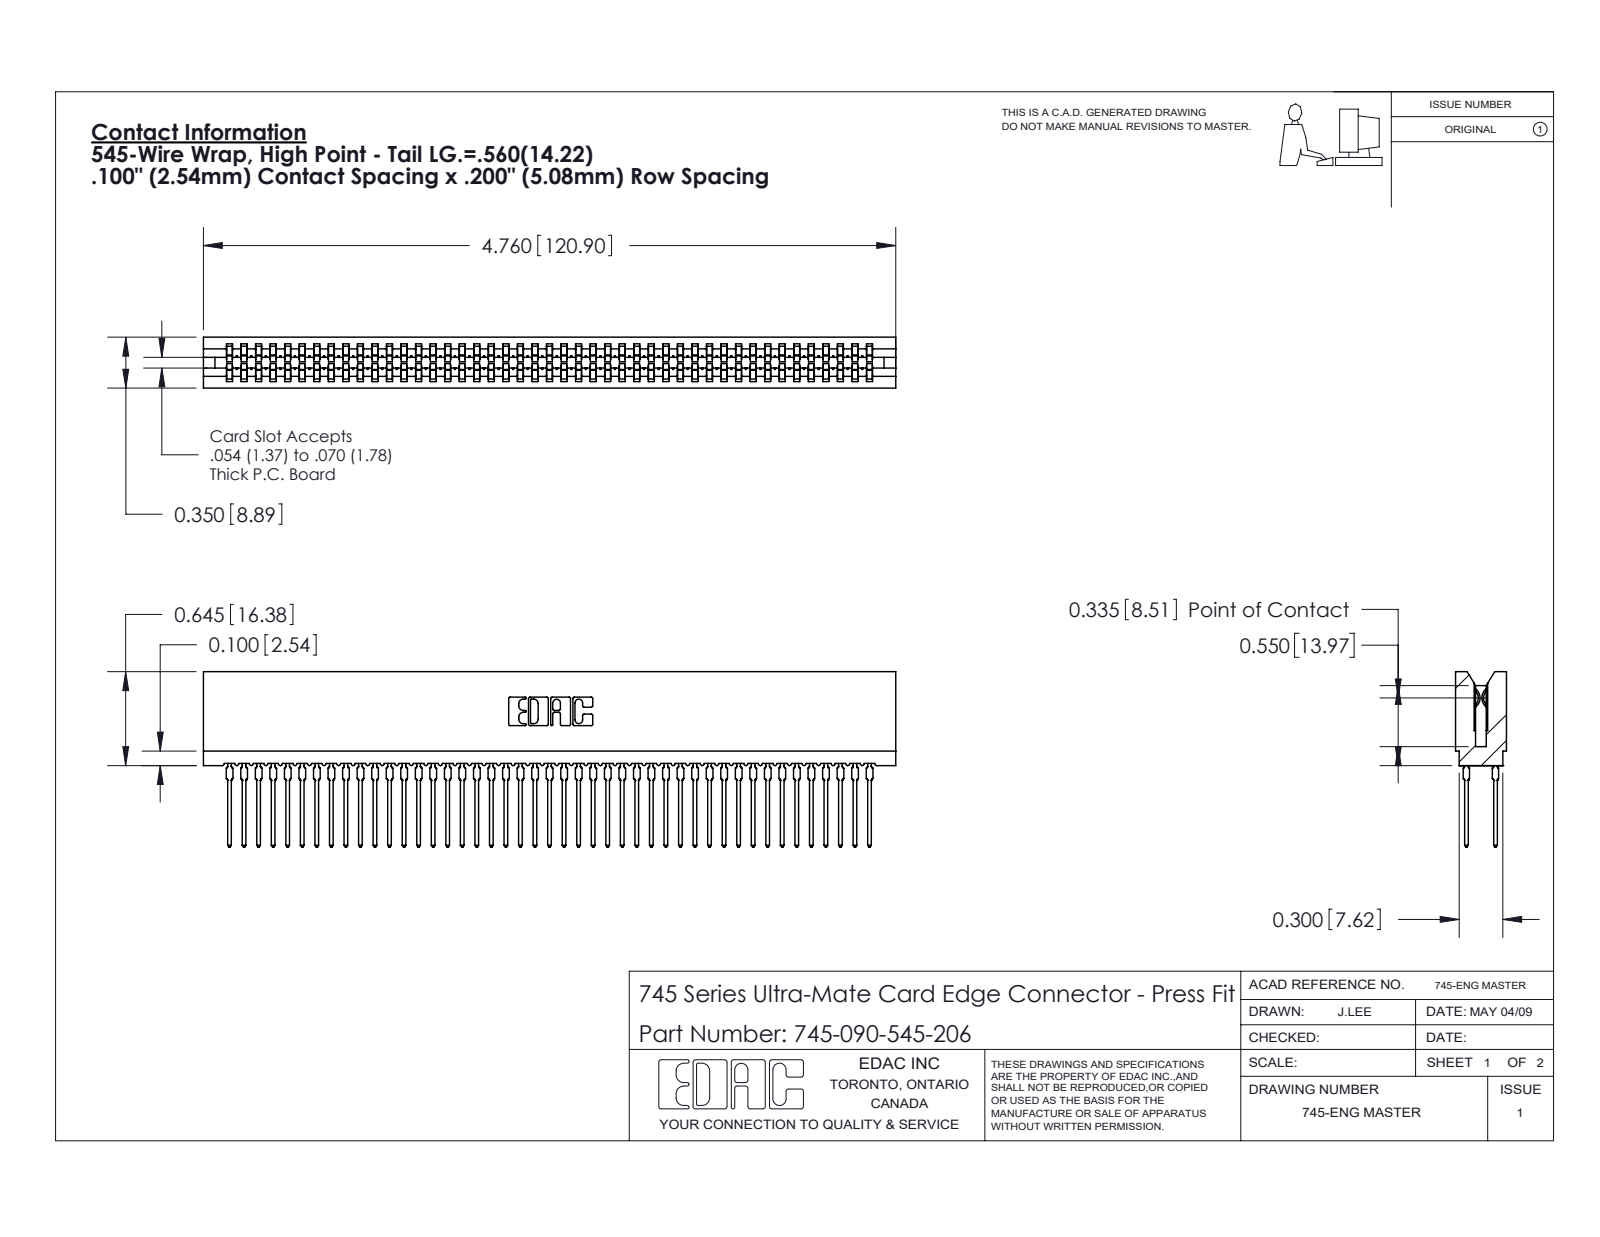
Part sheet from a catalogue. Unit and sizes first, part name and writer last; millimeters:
Units: millimetres
Overall size (bounding box): 120.9 × 30.6 × 8.9
Partial cylindrical surfaces — rounded edges, fillets, slot ends (radius × count): R0.5 ×180, R0.4 ×90, R0.3 ×22, R0.1 ×8, R0.3 ×8, R0.2 ×6, R0.8 ×6, R0.7 ×3
Main face-to-face distances: 1.6, 7.3, 8.9, 5.1, 1.1, 7.7, 0.5, 6.2, 3.5, 5.4
Volume: 11 200 mm³ · Surface area: 24 160 mm²
Bodies: 91 solids, 8151 faces (4196 planar, 1615 cylindrical, 2340 other)
Part name (STEP PRODUCT): 745-090-545-206; 745-292-001_545; 745 Part_Insulator Option - 06
STEP written by: SolidWorks 2020 (CONFIG_CONTROL_DESIGN)
